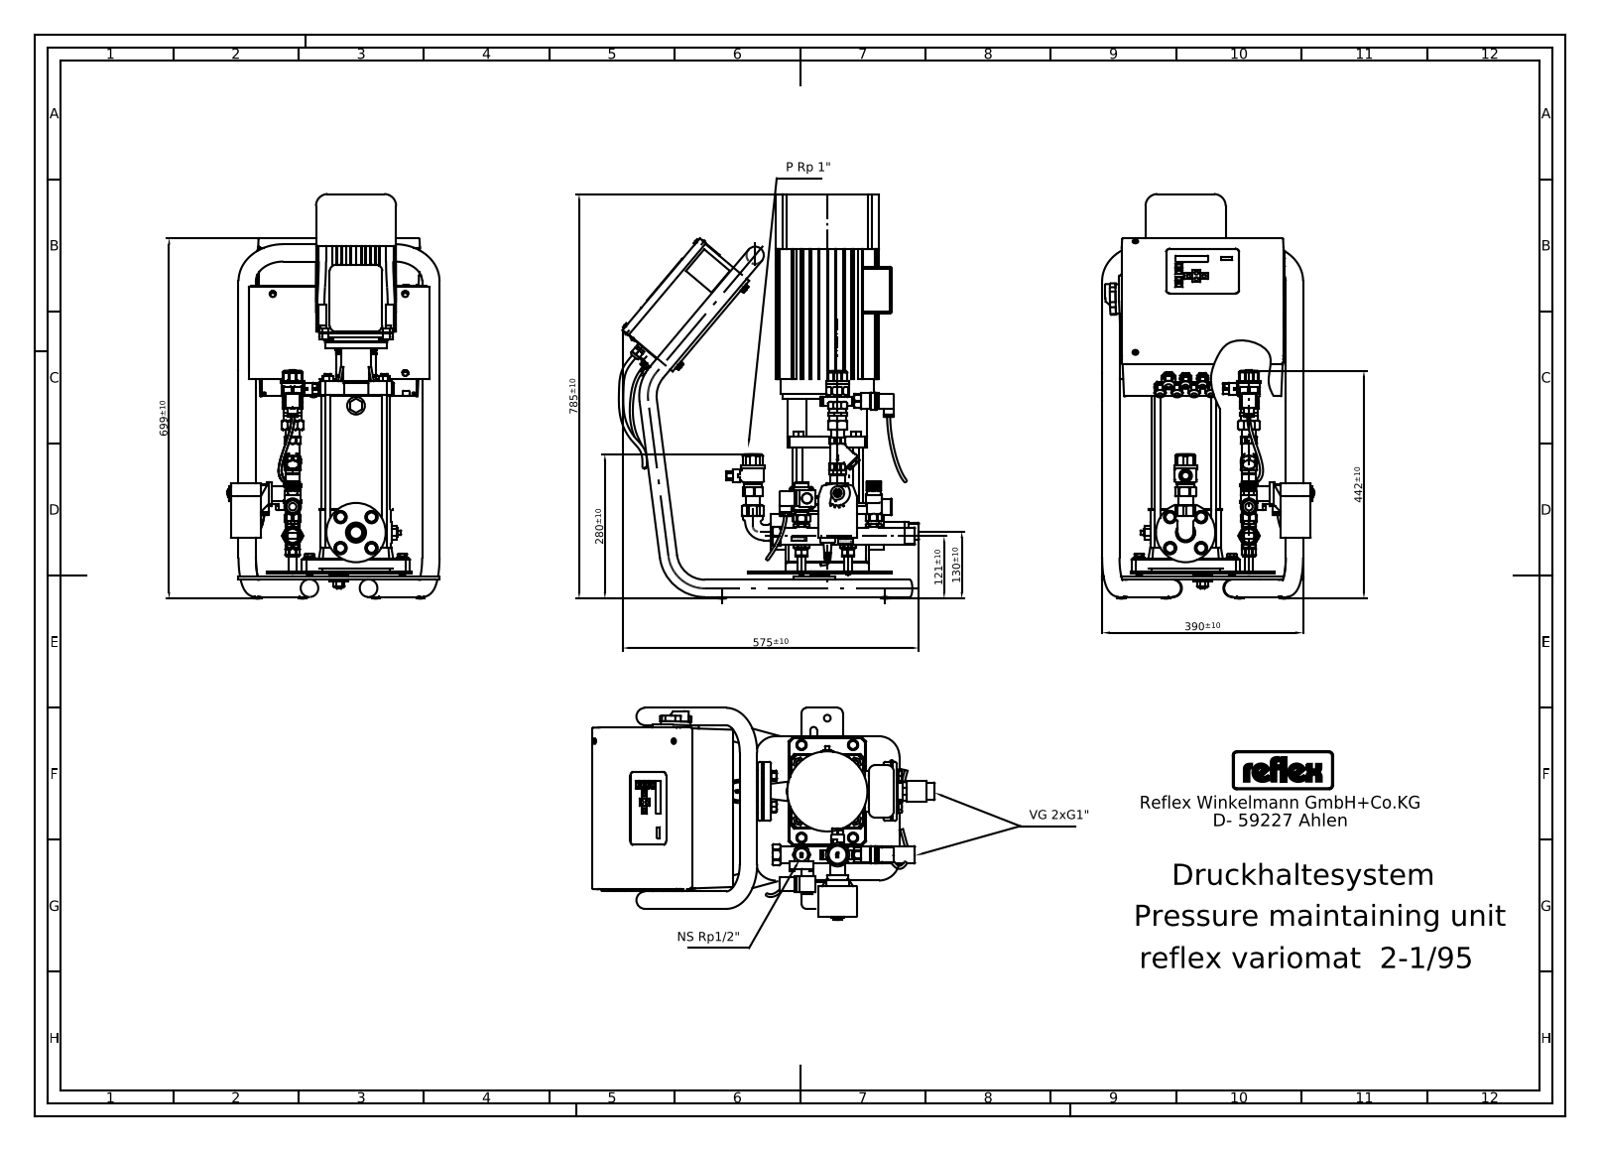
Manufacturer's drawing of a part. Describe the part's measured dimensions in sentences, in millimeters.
Its 3-D file was written by "Mechanical Desktop 2008 (CONFIG_CONTROL_DESIGN)". It is 60 solids with 2176 faces: 1280 planar, 752 cylindrical and 144 other. Overall it measures 761 by 655.27 by 411.5 millimeters. Its volume is 29 270 000 cubic millimeters and its surface area 2 166 000 square millimeters. Round holes: 11 of diameter 10.5, 8 of diameter 6, 4 of diameter 8, 4 of diameter 11, 1 of diameter 6.5, 1 of diameter 13.5, 1 of diameter 27, 1 of diameter 30.29, 1 of diameter 45, 1 of diameter 102. Round bosses or shafts: 12 of diameter 19, 10 of diameter 17.5, 7 of diameter 20, 6 of diameter 33.7, 5 of diameter 20.6, 5 of diameter 12, 4 of diameter 26, 4 of diameter 11. Partial cylindrical surfaces (rounded edges, fillets, slot ends): 65 of radius 280, 64 of radius 278, 47 of radius 1, 15 of radius 5, 12 of radius 10, 6 of radius 3, 6 of radius 7.5, 5 of radius 8. The main face-to-face distances are 2, 2.01, 4, 6, 344, 29, 10, 12, 16, 124. The hole center spacings are 32.07, 33, 56.63, 66, 86.96, 99, 16.86, 102.96.
